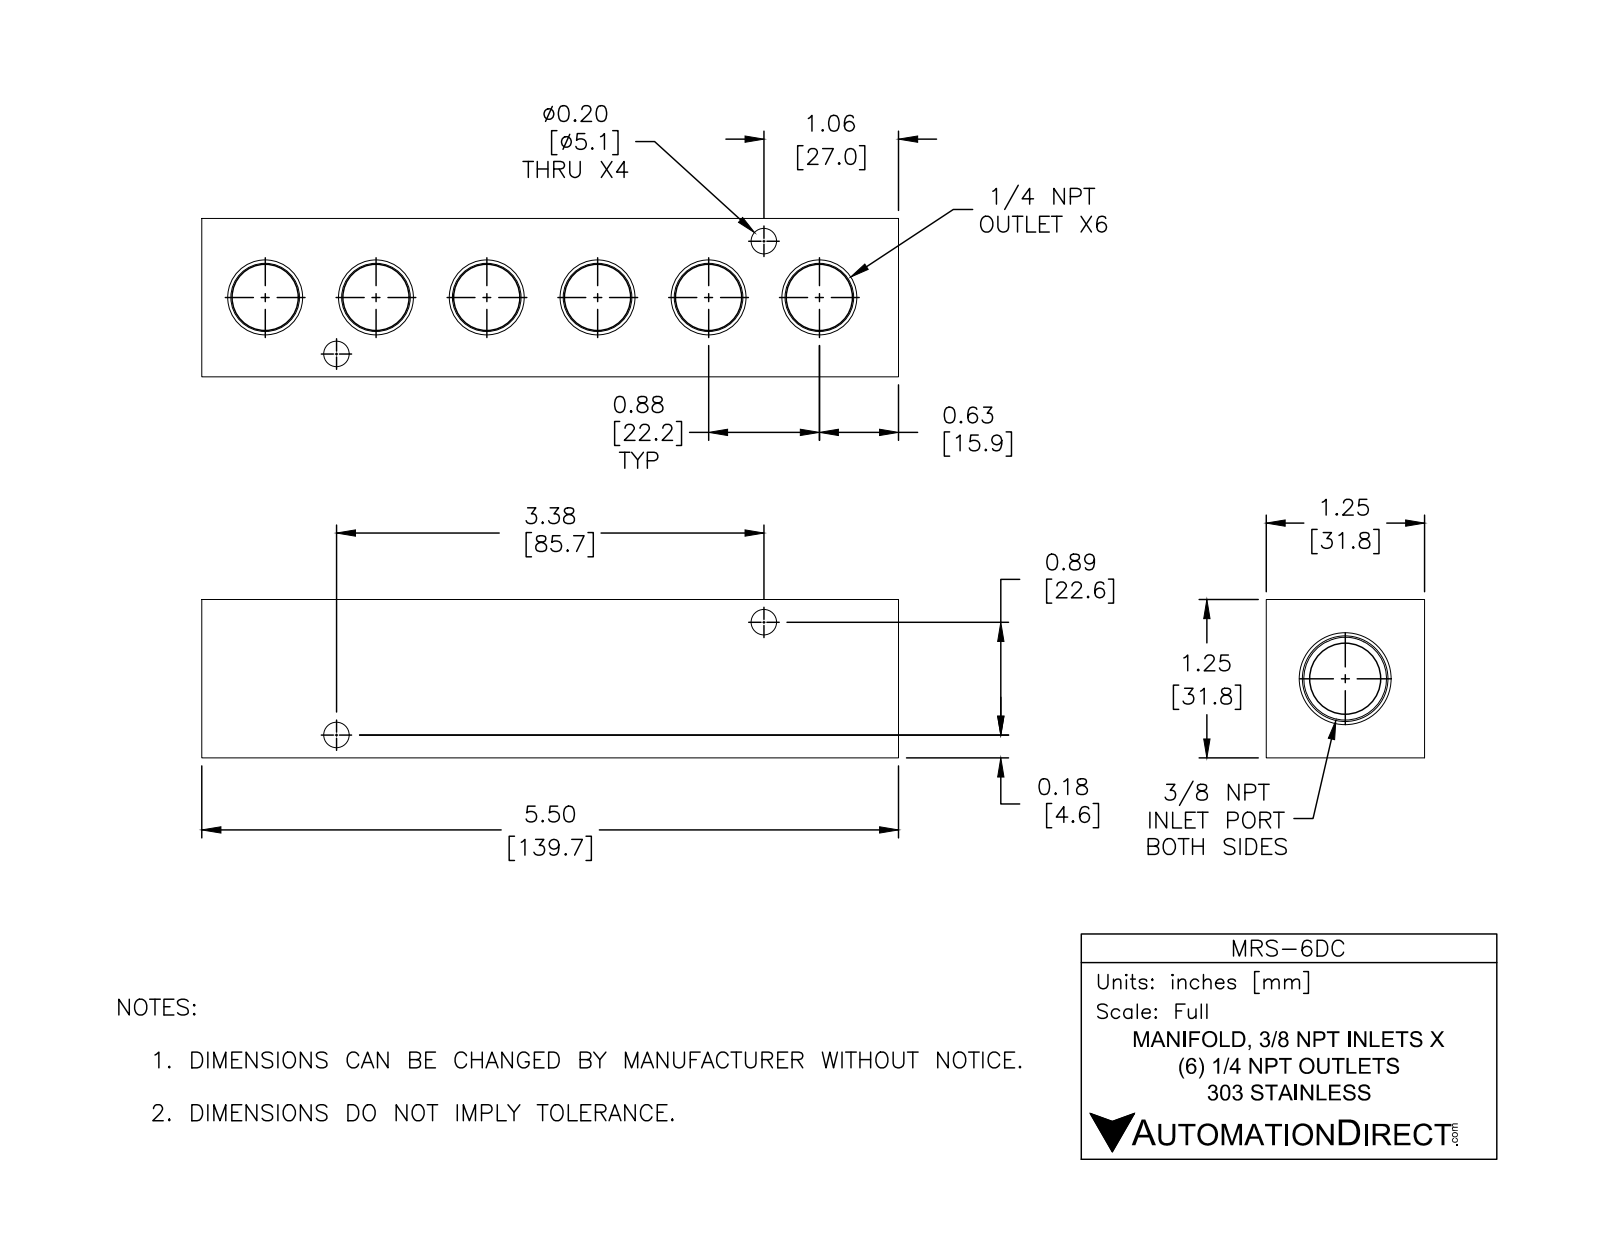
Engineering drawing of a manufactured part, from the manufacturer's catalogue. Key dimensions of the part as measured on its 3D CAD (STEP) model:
Part name (STEP PRODUCT): MRS-6DC
STEP written by: SolidWorks 2015 (CONFIG_CONTROL_DESIGN)
Units: inches
Bodies: 1 solid, 82 faces (20 planar, 30 cylindrical, 32 other)
Overall size (bounding box): 5.625 × 1.25 × 1.25
Volume: 6.673 in³ · Surface area: 44.79 in²
Round holes (diameter × count): ⌀0.2 ×4, ⌀0.562 ×1
Partial cylindrical surfaces — rounded edges, fillets, slot ends (radius × count): R0.219 ×6
Main face-to-face distances: 1.25, 5.625, 0.86, 0.39, 0.41, 5.215, 4.805
Hole centre spacings: 3.611
